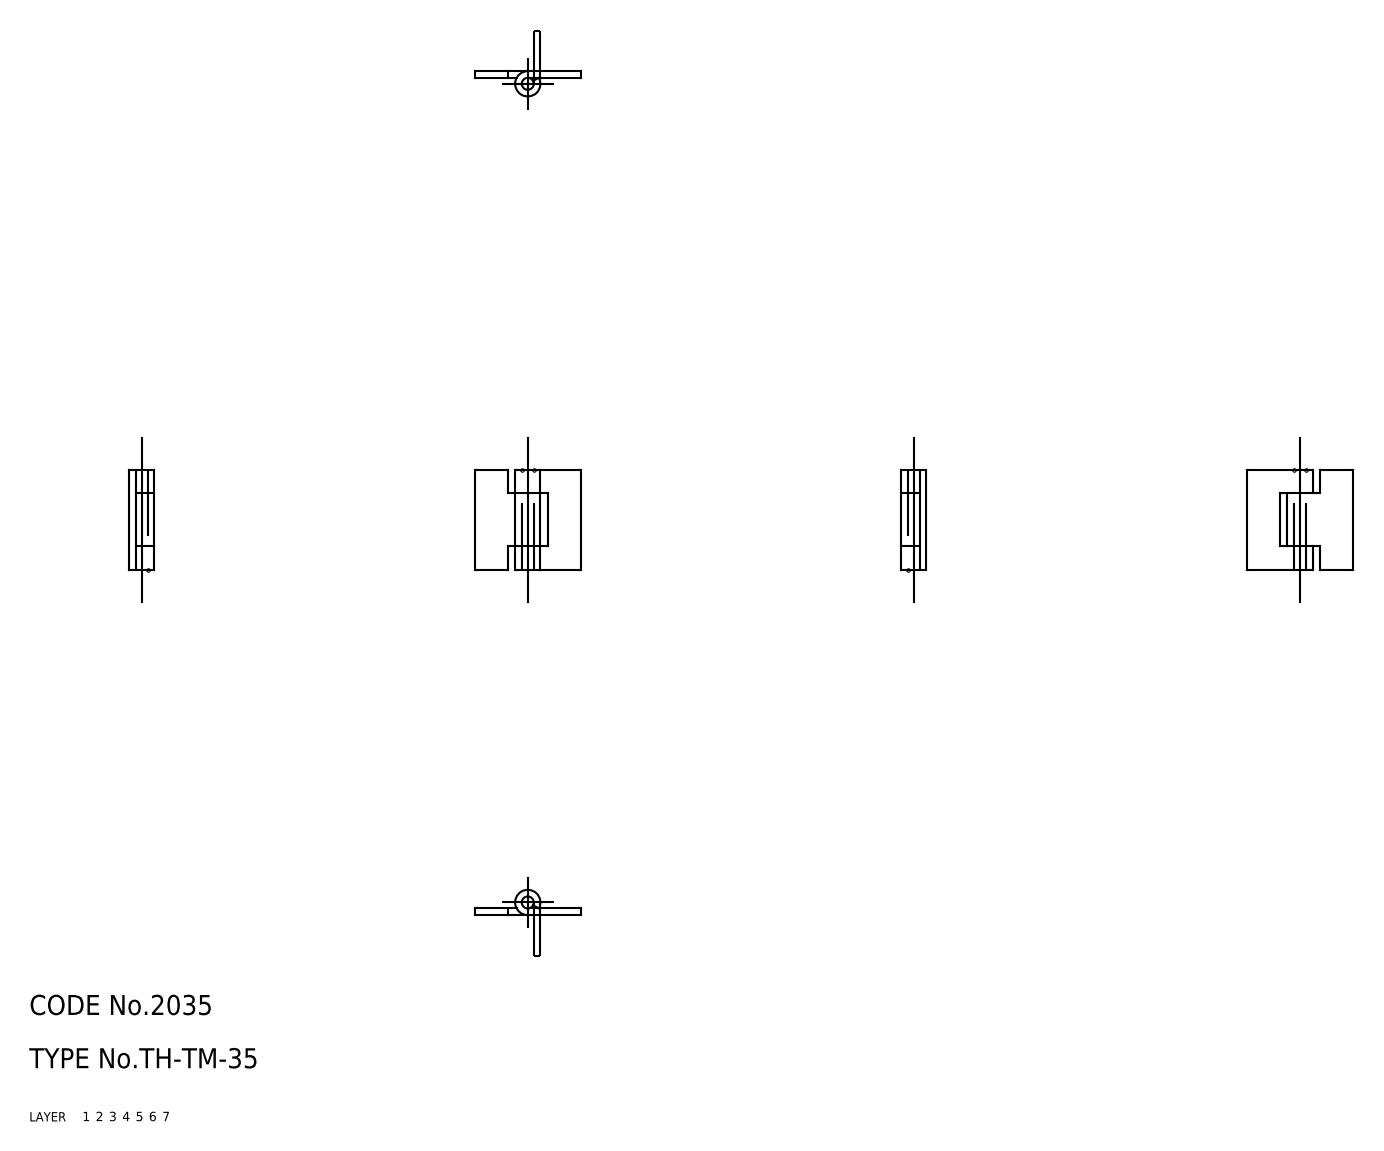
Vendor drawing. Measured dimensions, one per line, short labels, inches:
name: hinge piece_B; hinge piece_A; shaft; TH_TM_35_22885_36
written by: CADfix (AUTOMOTIVE_DESIGN)
unit: in
bodies: 3 solids, 30 faces (0 planar, 0 cylindrical, 30 other)
size: 0.63 × 0.591 × 0.15
volume: 0.021 in³; area: 1.3 in²
